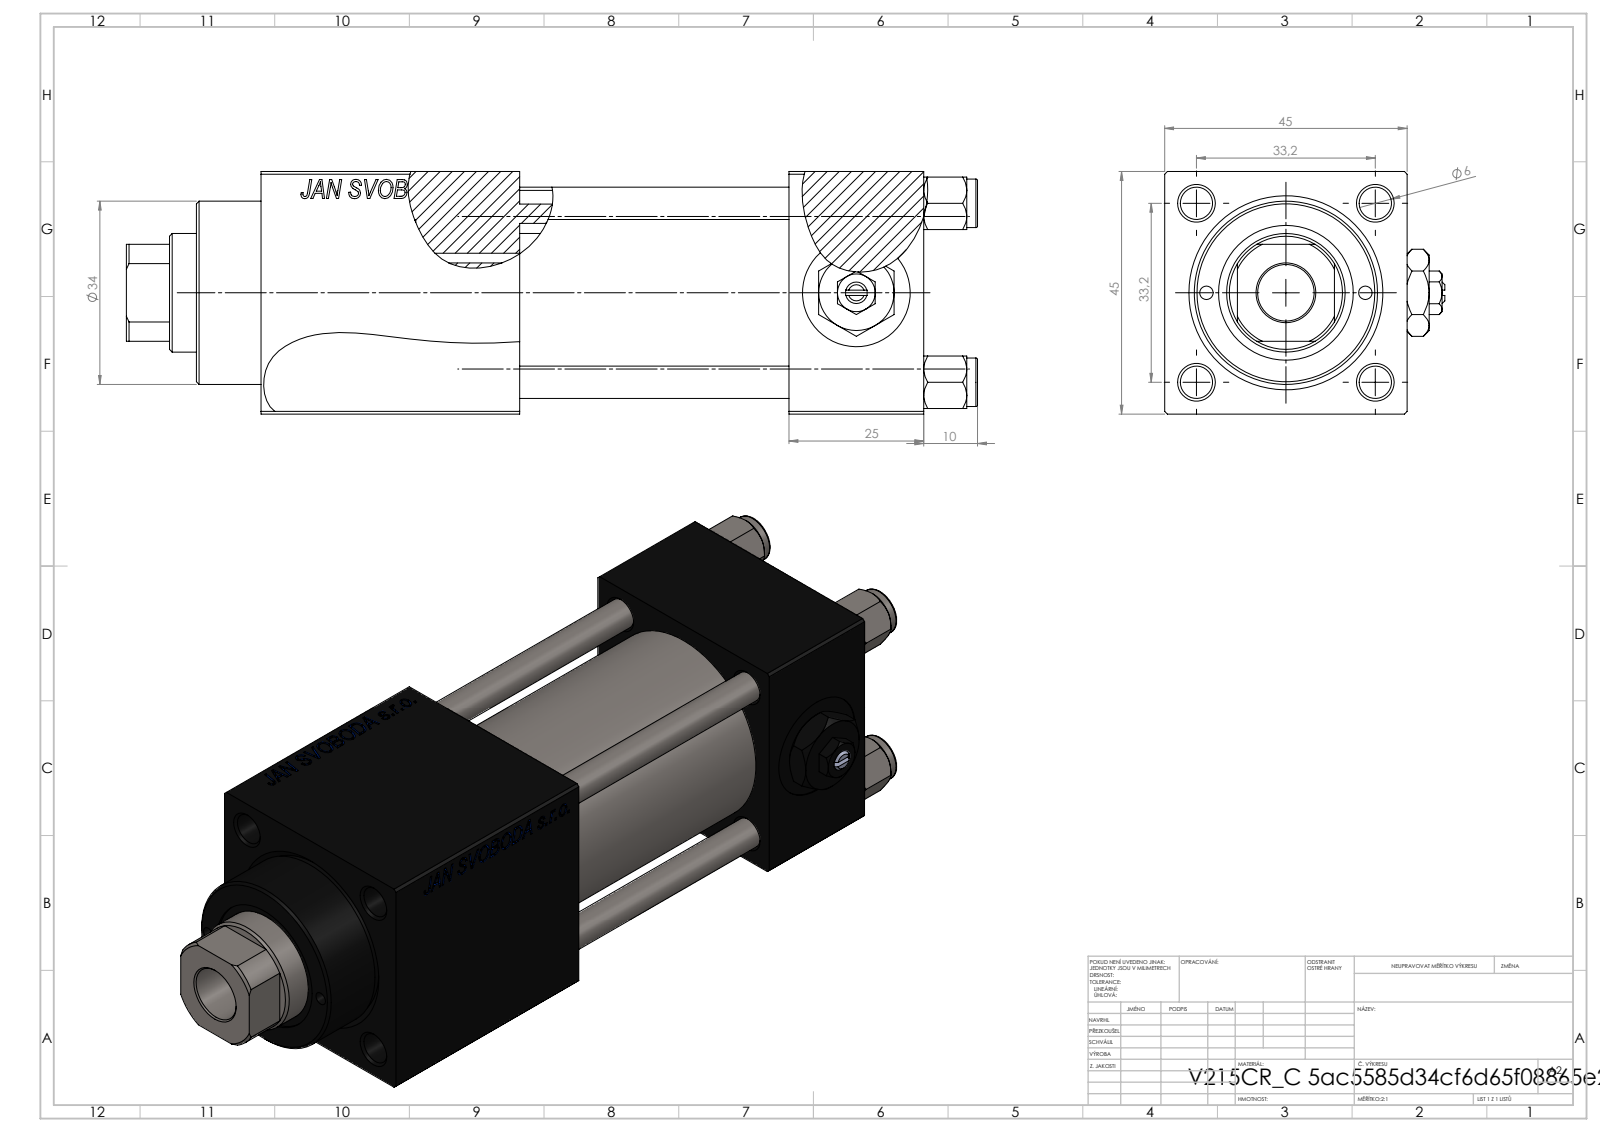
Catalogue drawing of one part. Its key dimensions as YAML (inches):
part_name: "V215CR_C_Body; V215_VC_A; Zatka_pro_OIL_PORT; V215CR_VCP_C (+2 more)"
step_written_by: "SolidWorks 2019 (CONFIG_CONTROL_DESIGN)"
units: inches
bodies: {solids: 12, faces: 1206, planar: 550, cylindrical: 98, other: 558}
overall_size: [6.22, 2.047, 1.772]
volume: 12.74
surface_area: 112.6
round_holes:
  - {diameter: 0.236, count: 4}
  - {diameter: 0.098, count: 2}
  - {diameter: 0.276, count: 2}
  - {diameter: 0.518, count: 2}
  - {diameter: 0.787, count: 2}
  - {diameter: 0.413, count: 1}
  - {diameter: 0.866, count: 1}
  - {diameter: 0.945, count: 1}
  - {diameter: 0.984, count: 1}
  - {diameter: 1.26, count: 1}
  - {diameter: 1.299, count: 1}
round_bosses_or_shafts:
  - {diameter: 0.354, count: 4}
  - {diameter: 1.496, count: 1}
  - {diameter: 1.339, count: 1}
partial_cylinders:
  - {radius: 0.413, count: 1}
face_to_face_distances: [1.772, 0.984, 1.969, 4.843, 2.953, 3.858, 1.89, 3.713, 2.728, 0.76]
hole_center_spacings: [0.657, 0.924, 1.307, 1.396, 0.581, 1.848, 1.161, 2.972]
